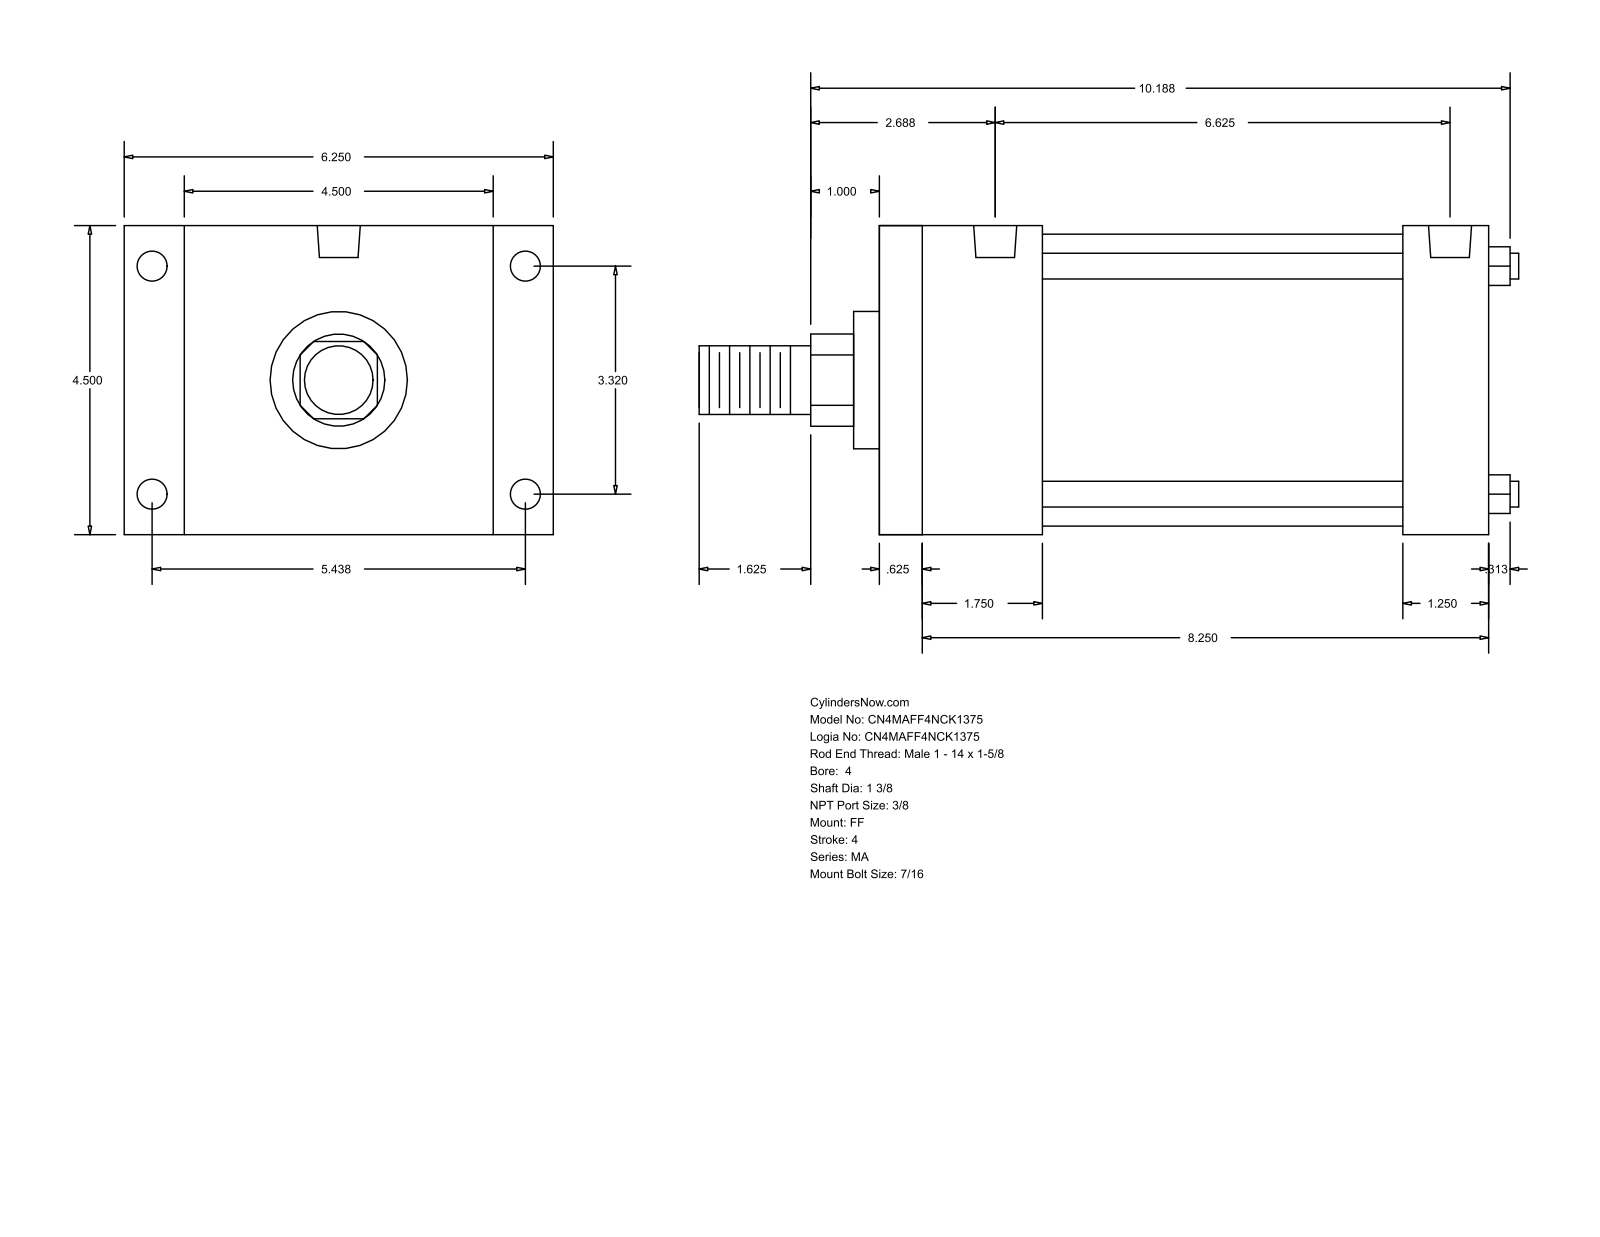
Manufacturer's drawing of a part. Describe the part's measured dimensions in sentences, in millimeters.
The part is named "MA_FF__0400_1.375". Its 3-D file was written by "GSSL Pune (CONFIG_CONTROL_DESIGN)". It is 0 solids with 92 faces: 64 planar, 28 cylindrical and 0 other. Overall it measures 303.21 by 158.75 by 114.3 millimeters. Round holes: 8 of diameter 11.11, 2 of diameter 15.93. Round bosses or shafts: 4 of diameter 9.53, 1 of diameter 107.95, 1 of diameter 50.8, 1 of diameter 34.92, 1 of diameter 25.4. Partial cylindrical surfaces (rounded edges, fillets, slot ends): 1 of radius 17.06. The main face-to-face distances are 114.3, 225.42, 15.87, 209.55, 22.23, 136.53, 193.67, 177.8, 31.75, 60.32. The hole center spacings are 84.32, 138.12, 158.75, 161.82, 4.76, 4.77, 163.51, 163.52.
